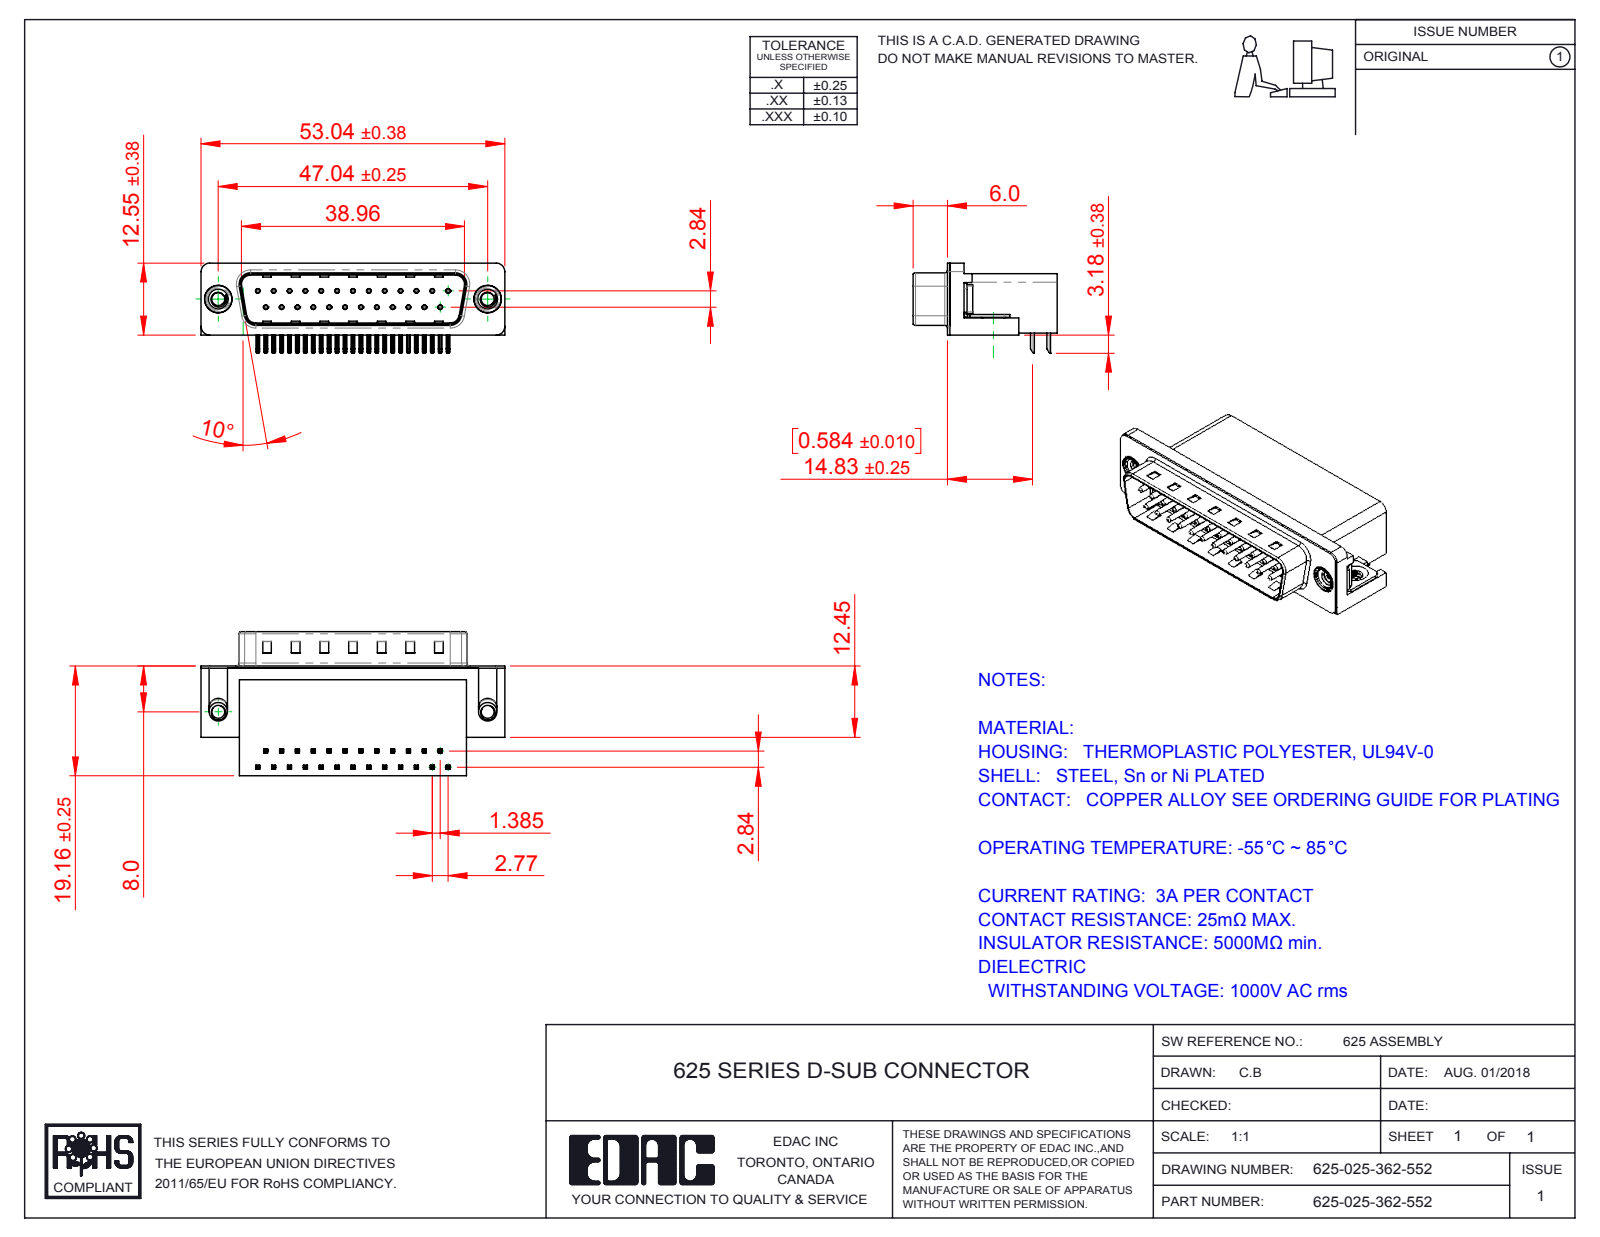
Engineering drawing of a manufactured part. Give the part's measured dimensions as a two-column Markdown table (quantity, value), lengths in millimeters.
| quantity | value |
| --- | --- |
| part name | 625 Shell_25 Socket; 625 Housing_25 Socket; 625 Contact Bottom; 625 Contact Top (+3 more) |
| STEP written by | SolidWorks 2016 (CONFIG_CONTROL_DESIGN) |
| units | millimeters |
| bodies | 31 solids, 2297 faces (1407 planar, 673 cylindrical, 217 other) |
| overall size | 53.04 × 25.16 × 15.73 |
| volume | 9 177 mm³ |
| surface area | 8 941 mm² |
| round holes (diameter × count) | 0.35 × 25, 0.8 × 25, 2.26 × 4, 4 × 2, 4.8 × 2, 5 × 2 |
| round bosses / shafts (diameter × count) | 0.75 × 25, 4.9 × 2, 4.75 × 2, 3.9 × 2, 3.26 × 2 |
| partial cylindrical surfaces (radius × count) | 0.25 × 108, 0.12 × 50, 1 × 16, 0.5 × 9, 1.6 × 8, 1.5 × 7, 0.9 × 4, 2 × 4 |
| main face-to-face distances | 0.4, 10.35, 18.76, 2.1, 8.76, 10.46, 10.86, 1.7, 19.16, 10.11 |
| hole center spacings | 3.16, 2.77, 11.08, 5.54, 8.31, 5.03, 13.85, 7.48 |
